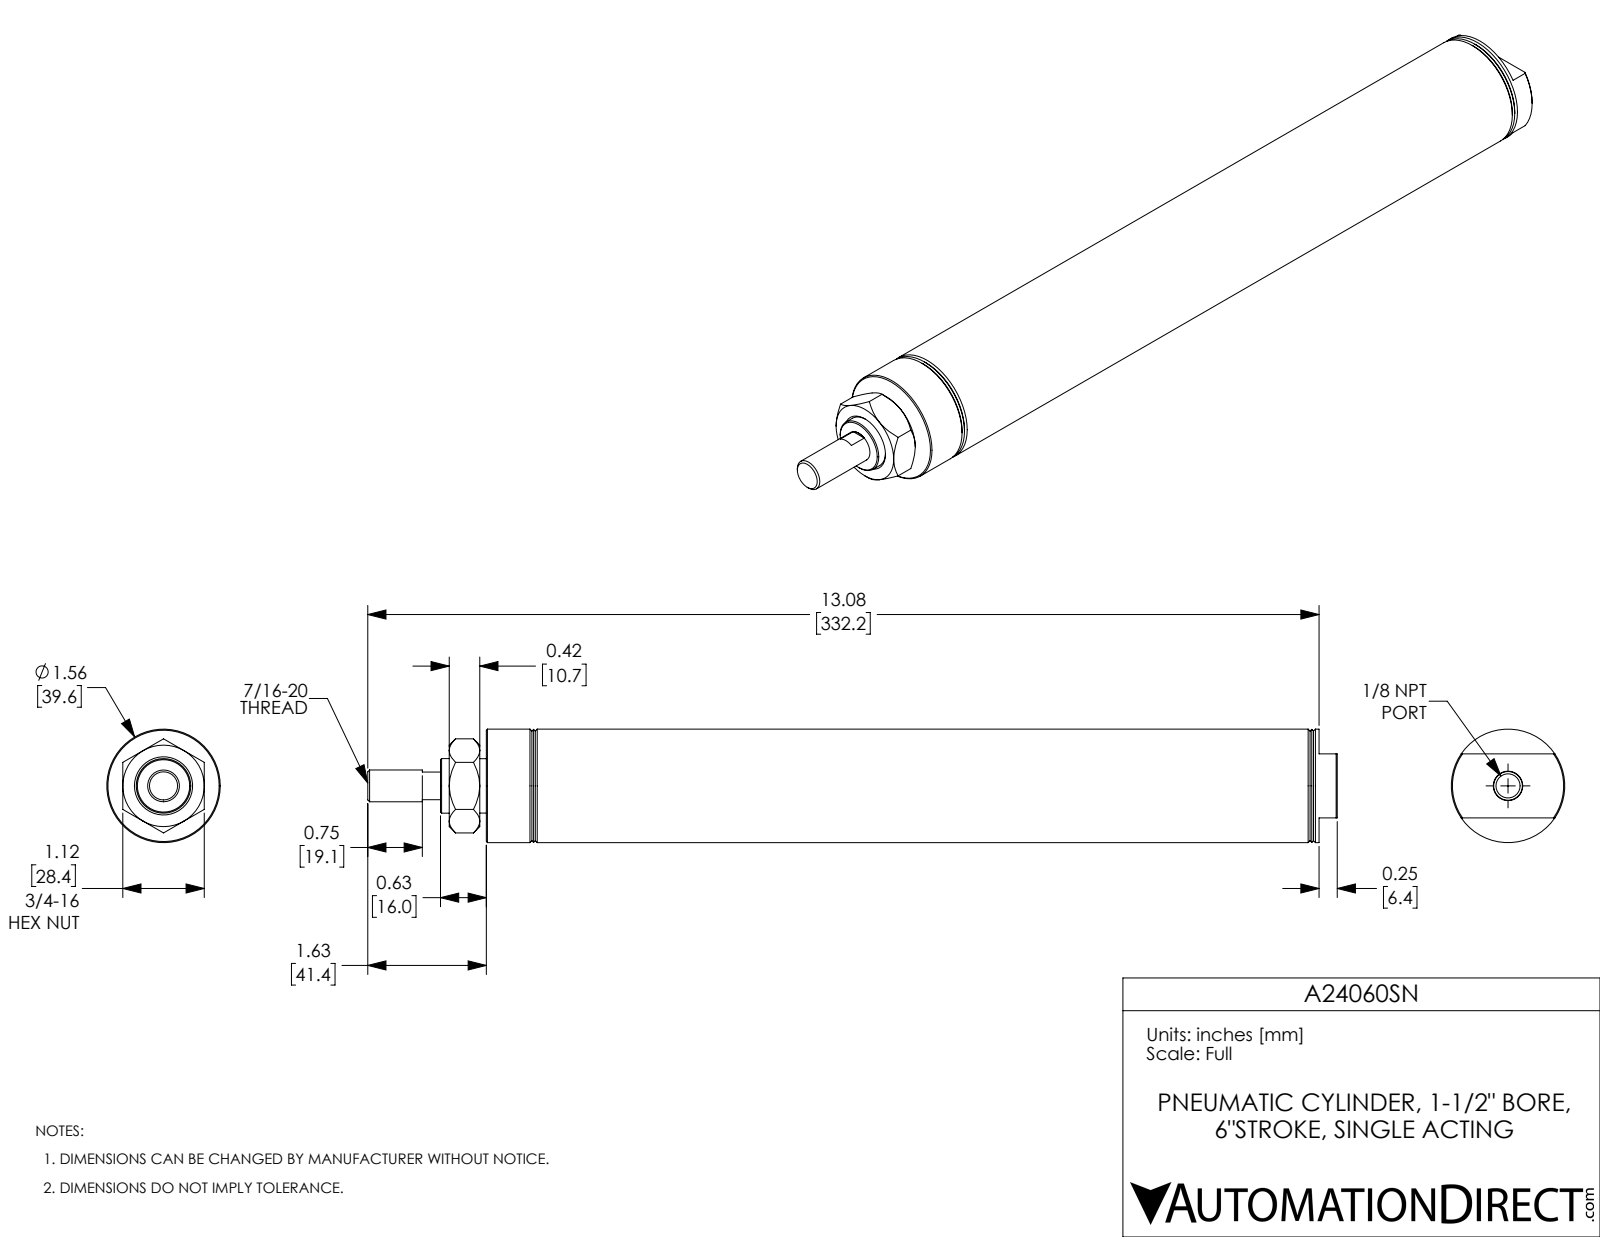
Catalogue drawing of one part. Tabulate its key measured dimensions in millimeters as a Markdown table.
| quantity | value |
| --- | --- |
| part name | A24060SN; A24060SN_Mounting Nut_D-3556; A24060SN-Rod; A24060SN-MainBody |
| STEP written by | SolidWorks 2017 (AUTOMOTIVE_DESIGN) |
| units | millimeters |
| bodies | 3 solids, 93 faces (28 planar, 22 cylindrical, 43 other) |
| overall size | 338.6 × 39.6 × 39.6 |
| volume | 212 200 mm³ |
| surface area | 82 130 mm² |
| round holes (diameter × count) | 8.4 × 1, 11.1 × 1, 19.1 × 1, 38.1 × 1 |
| round bosses / shafts (diameter × count) | 39.6 × 1, 19 × 1 |
| main face-to-face distances | 66, 231.1, 12.7, 165.1, 152.4, 218.4, 78.7, 297.2, 6.4, 28.4 |
